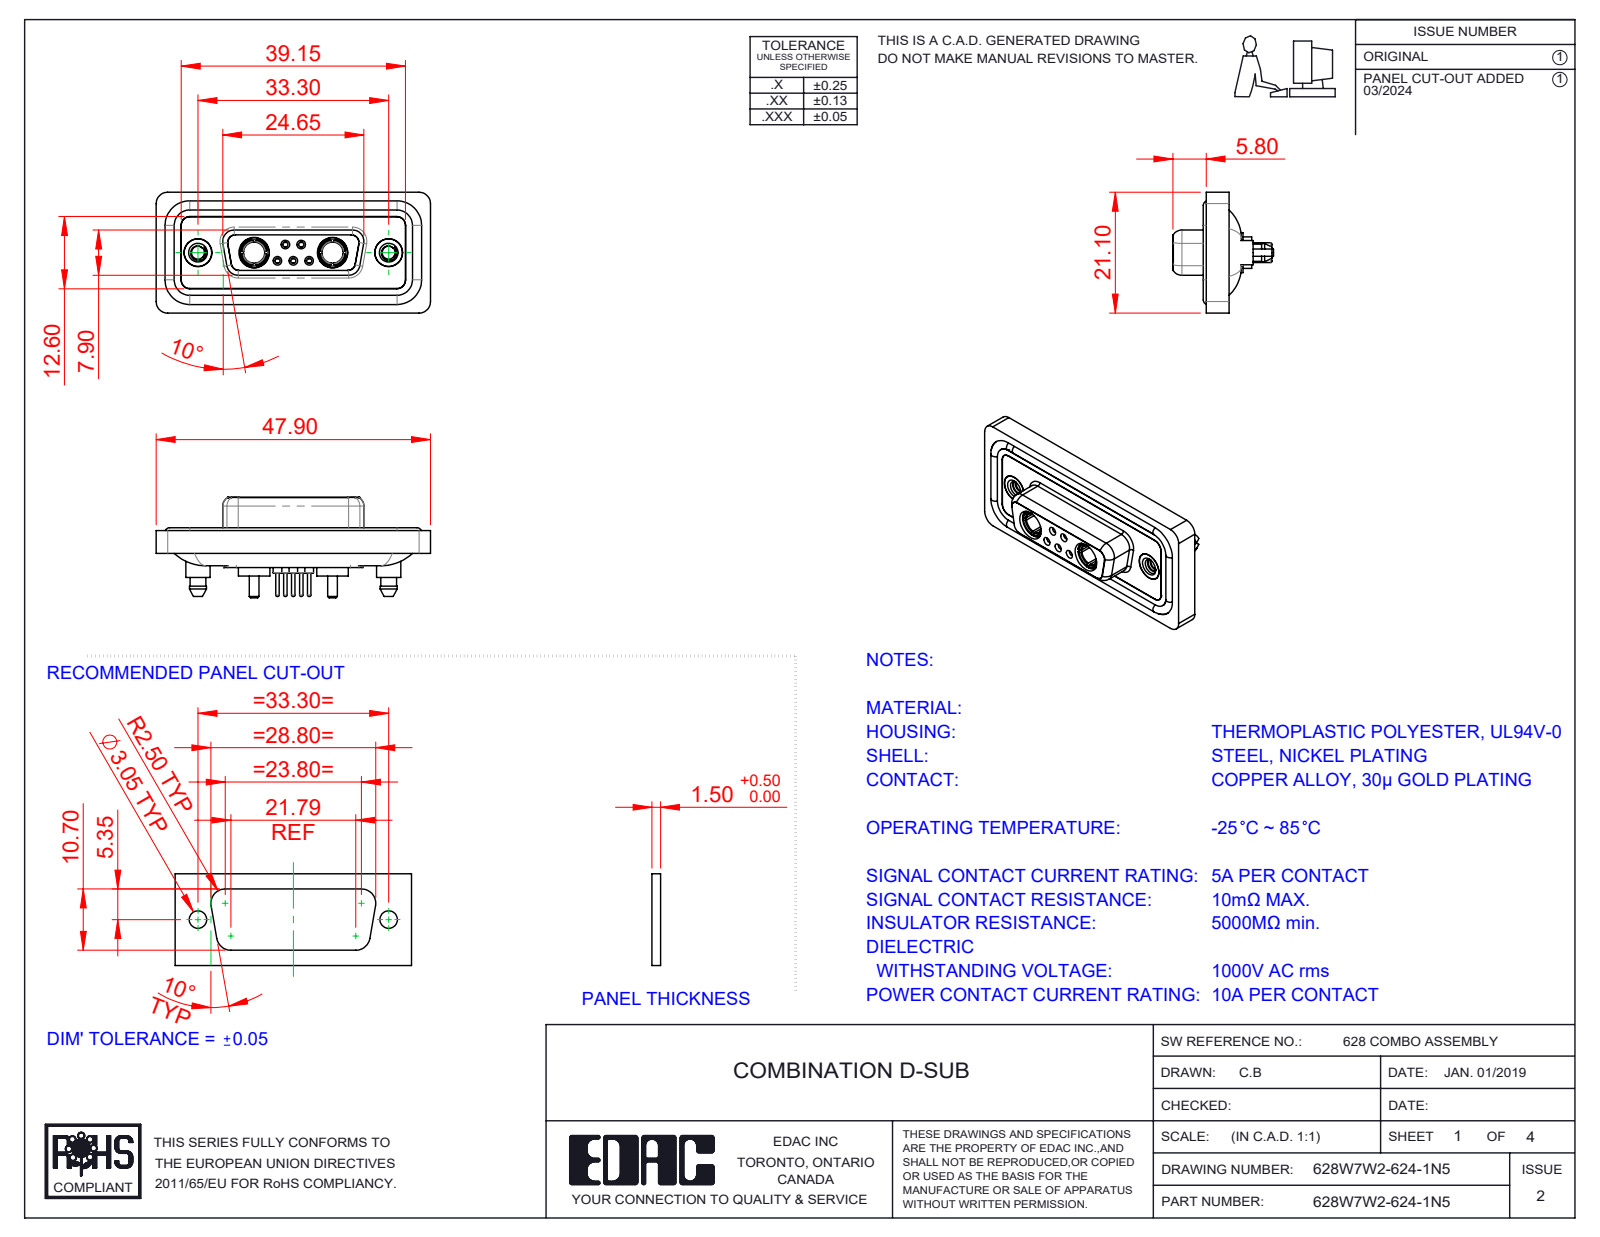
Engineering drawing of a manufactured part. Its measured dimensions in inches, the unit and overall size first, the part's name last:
Units: inches
Overall size (bounding box): 1.886 × 0.831 × 0.691
Round holes (diameter × count): ⌀0.035 ×5, ⌀0.043 ×5, ⌀0.059 ×5, ⌀0.079 ×5, ⌀0.191 ×4, ⌀0.063 ×3, ⌀0.067 ×2, ⌀0.089 ×2, ⌀0.146 ×2, ⌀0.157 ×2, ⌀0.159 ×2, ⌀0.197 ×2
Round bosses / shafts (diameter × count): ⌀0.063 ×6, ⌀0.087 ×5, ⌀0.024 ×5, ⌀0.217 ×2, ⌀0.213 ×2, ⌀0.205 ×2, ⌀0.195 ×2, ⌀0.195 ×2
Partial cylindrical surfaces — rounded edges, fillets, slot ends (radius × count): R0.059 ×24, R0.079 ×20, R0.053 ×12, R0.063 ×10, R0.01 ×4, R0.02 ×4, R0.024 ×4, R0.026 ×4
Main face-to-face distances: 0.016, 0.071, 0.063, 0.02, 0.114, 0.043, 0.293, 0.222, 0.26, 0.278
Hole centre spacings: 0.124, 0.109, 0.386, 0.925, 0.17, 0.17, 0.198, 0.198
Volume: 0.377 in³ · Surface area: 15.8 in²
Bodies: 16 solids, 859 faces (254 planar, 361 cylindrical, 244 other)
Part name (STEP PRODUCT): Power Socket_10A S; 628W7W2-624-1N5; 628Combo Contact Row 2_24; 628Combo Shell Front_15 Contacts (+5 more)
STEP written by: SolidWorks 2023 (CONFIG_CONTROL_DESIGN)
